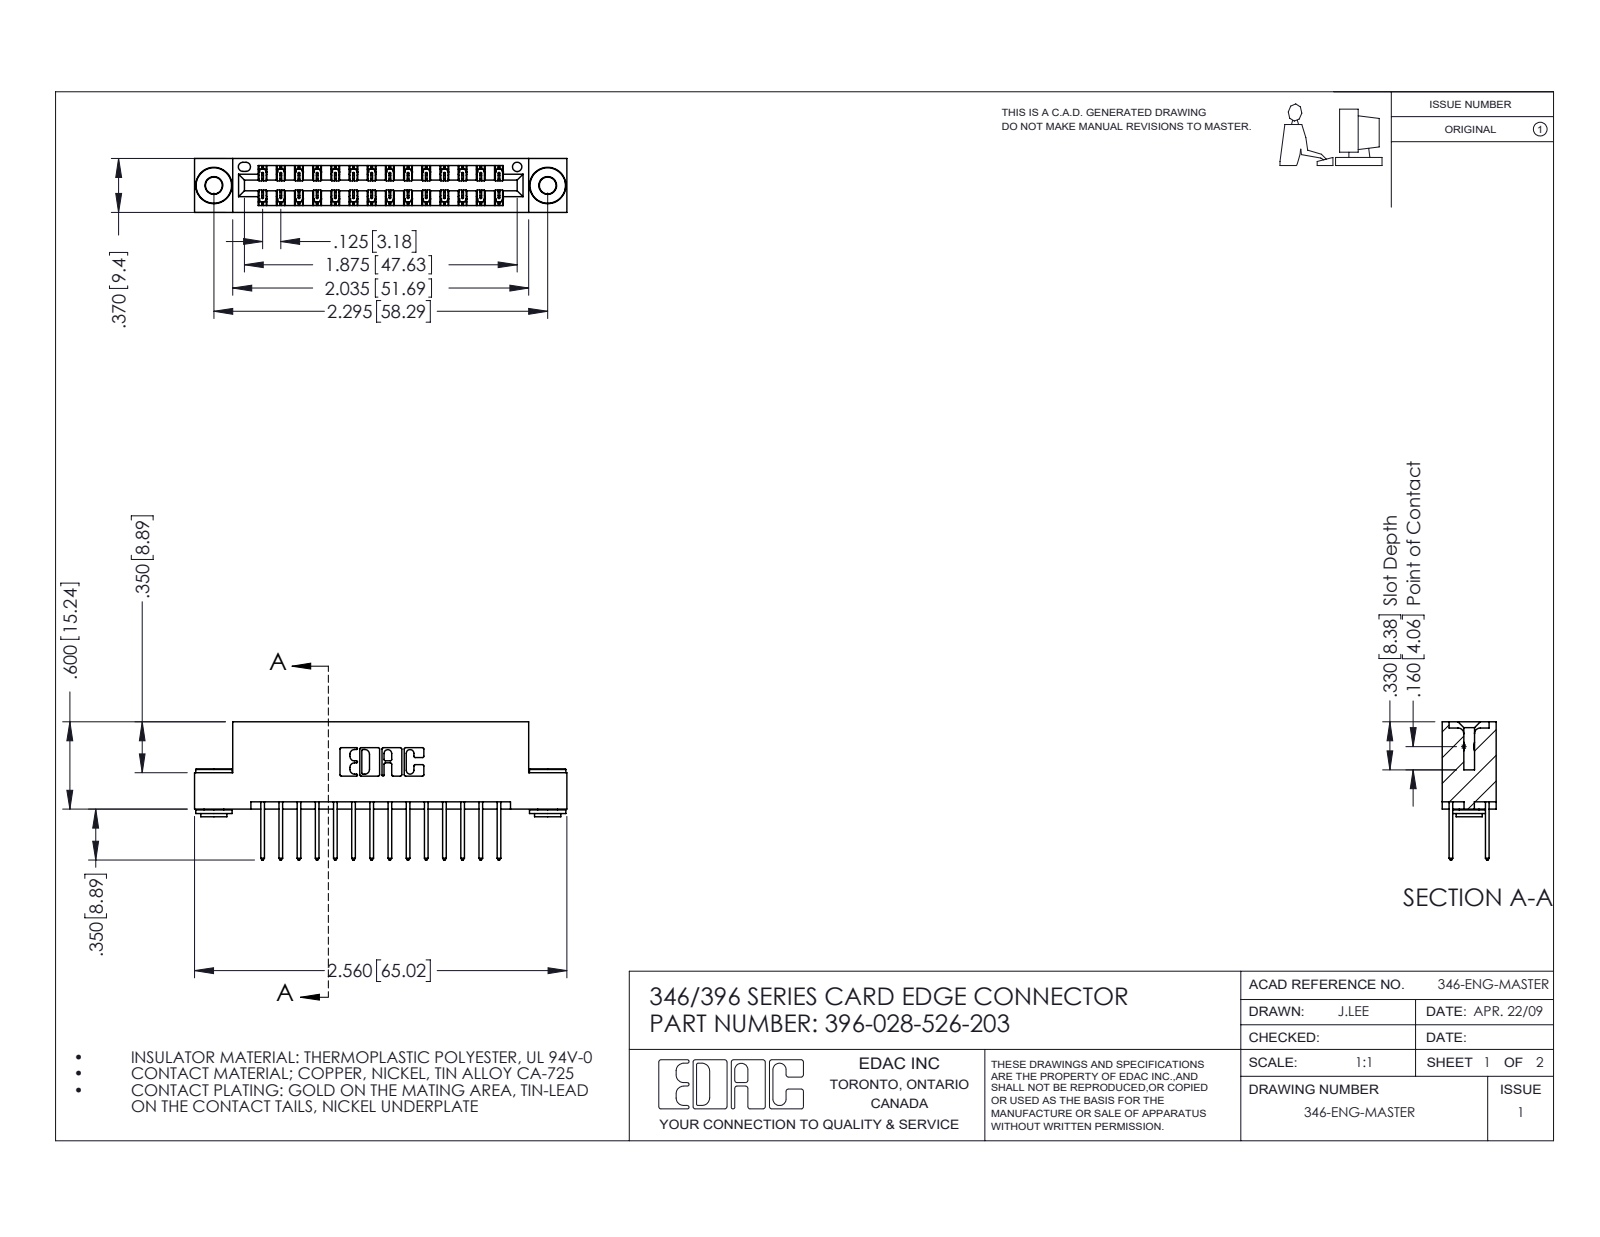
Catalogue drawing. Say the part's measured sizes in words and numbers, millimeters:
The part is named "345-250-002_345-250-002-102; 345-292-001_345-293-126; 346 Part_Flush Mounting Lugs - 0.156 Dia-TH; 396-028-526-203". Its 3-D file was written by "SolidWorks 2016 (CONFIG_CONTROL_DESIGN)". It is 31 solids with 1616 faces: 1066 planar, 542 cylindrical and 8 other. Overall it measures 65 by 24.1 by 9.4 millimeters. Its volume is 6 190 cubic millimeters and its surface area 8 484 square millimeters. Round holes: 2 of diameter 2.9, 2 of diameter 4, 1 of diameter 1.6. Round bosses or shafts: 2 of diameter 6.4, 2 of diameter 4.6, 2 of diameter 3.5. Partial cylindrical surfaces (rounded edges, fillets, slot ends): 42 of radius 0.2, 28 of radius 0.3, 22 of radius 0.3, 6 of radius 0.2, 6 of radius 0.8, 3 of radius 0.7, 2 of radius 0.4, 2 of radius 0.6. The main face-to-face distances are 6.4, 1.2, 8.2, 9.4, 0.6, 1.8, 7.6, 7, 3.8, 5.6. The hole center spacings are 6.2, 53.1, 58.3.
